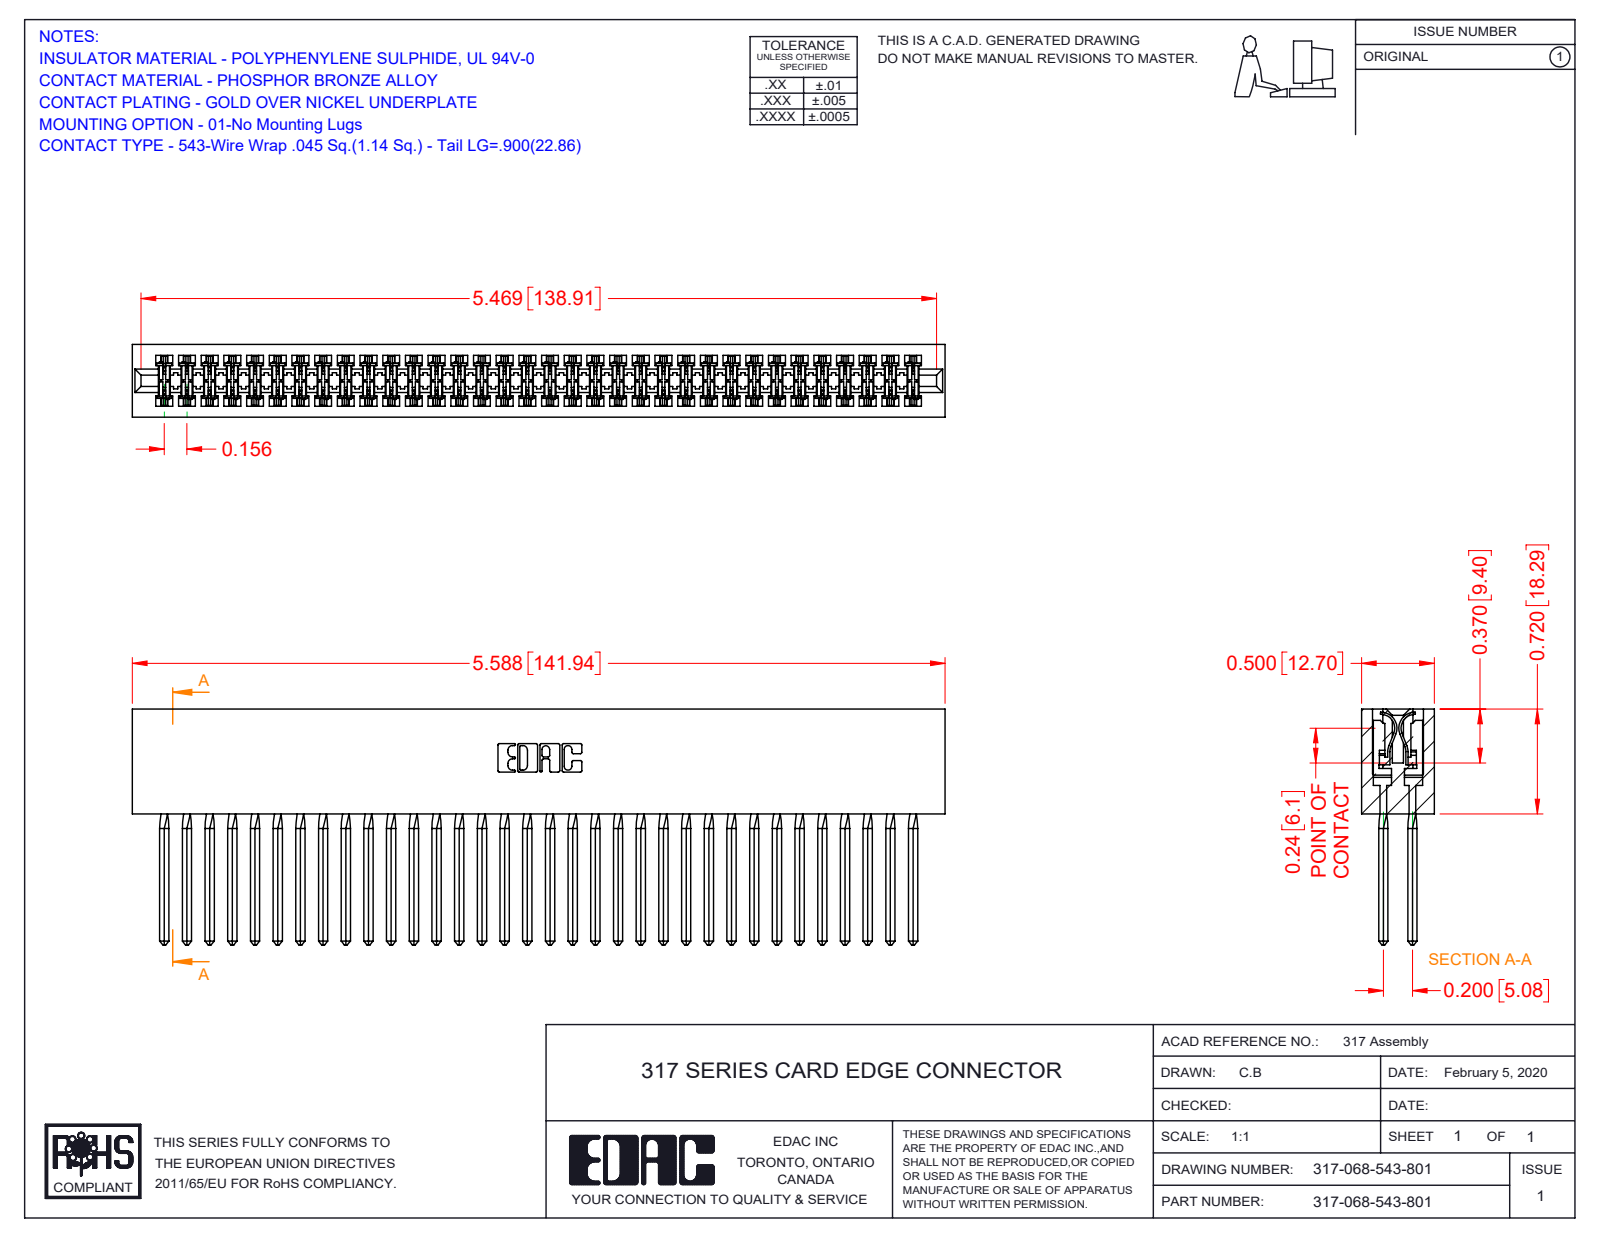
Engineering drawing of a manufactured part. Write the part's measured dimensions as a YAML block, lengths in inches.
part_name: "317-290-001_543; 317-068-543-801; 317 Part_Lugless"
step_written_by: "SolidWorks 2016 (CONFIG_CONTROL_DESIGN)"
units: inches
bodies: {solids: 69, faces: 6142, planar: 5014, cylindrical: 856, other: 272}
overall_size: [5.588, 1.62, 0.5]
volume: 1.567
surface_area: 60.33
partial_cylinders:
  - {radius: 0.015, count: 136}
  - {radius: 0.01, count: 22}
  - {radius: 0.007, count: 6}
  - {radius: 0.031, count: 6}
  - {radius: 0.026, count: 3}
  - {radius: 0.095, count: 2}
  - {radius: 0.1, count: 2}
  - {radius: 0.11, count: 2}
face_to_face_distances: [0.075, 0.5, 0.425, 0.35, 0.11, 0.195, 0.094, 0.2, 0.115, 0.131]
